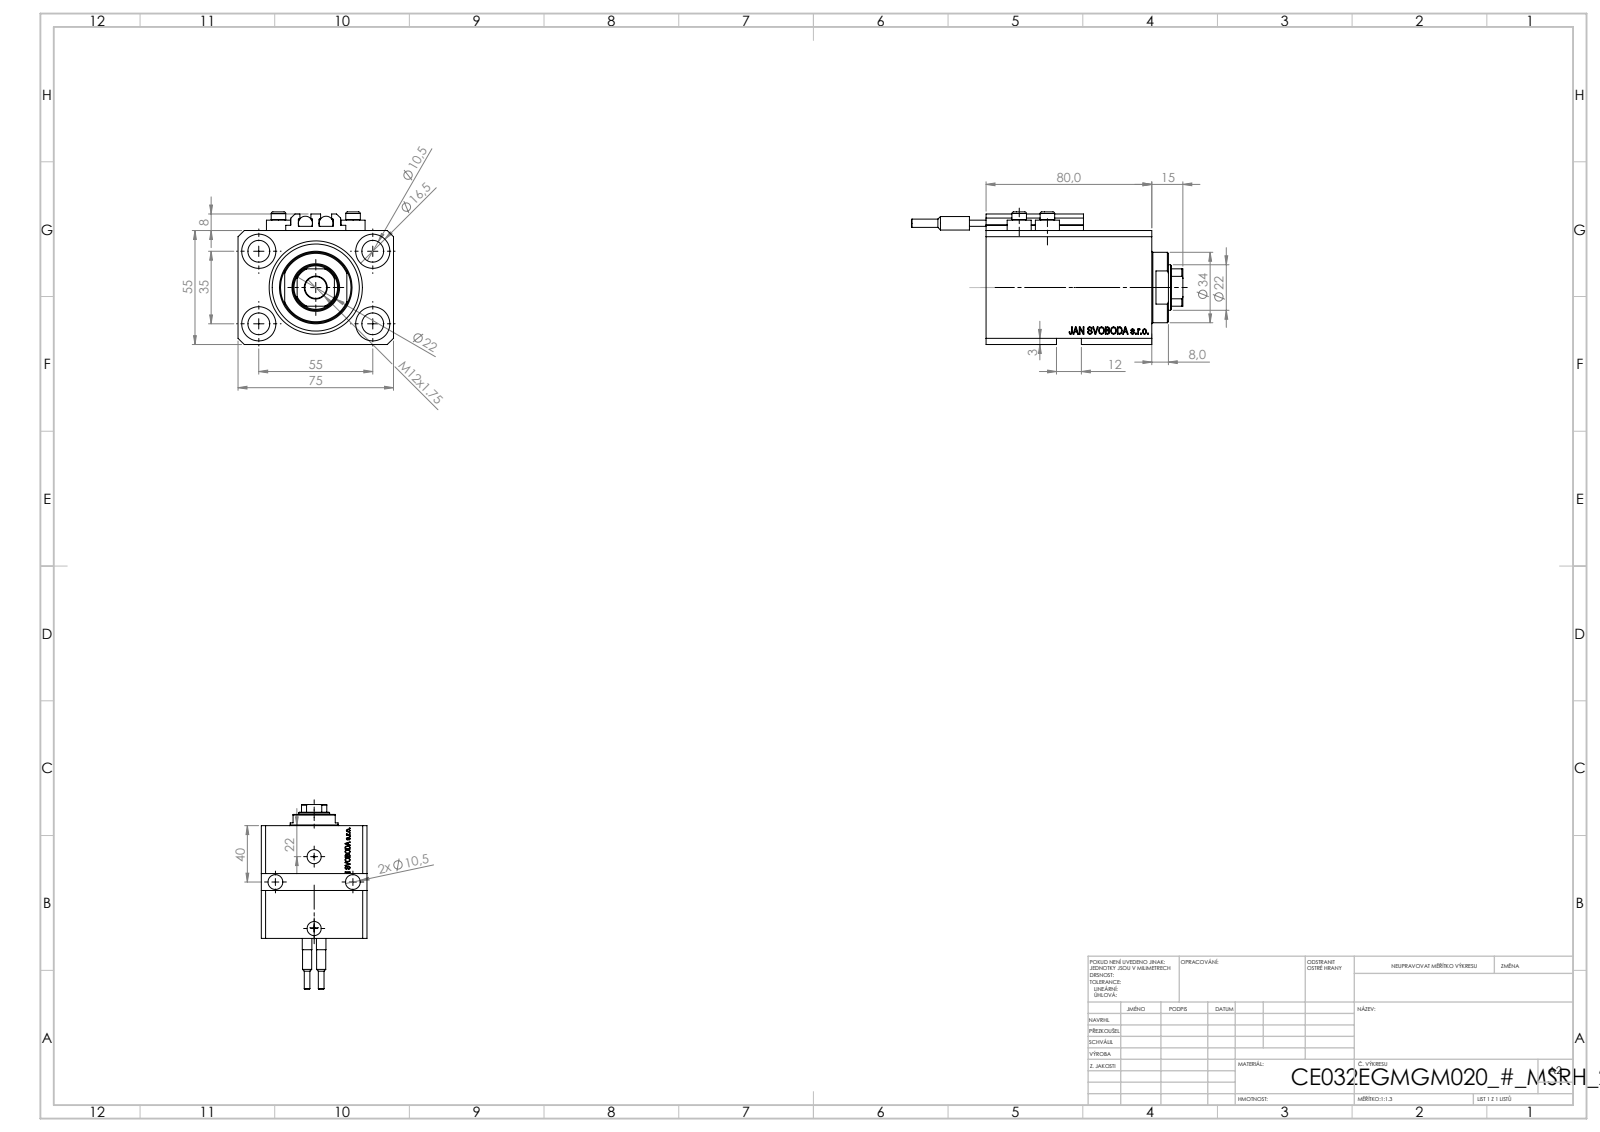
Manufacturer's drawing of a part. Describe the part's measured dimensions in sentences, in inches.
The part is named "ALLEN BOLT V250CE; V250CE_C_VCP; V250CE_E_Body; SWITCH_V250CE (+1 more)". Its 3-D file was written by "SolidWorks 2019 (CONFIG_CONTROL_DESIGN)". It is 10 solids with 1116 faces: 546 planar, 138 cylindrical and 432 other. Overall it measures 5.157 by 2.953 by 2.52 inches. Its volume is 17.54 cubic inches and its surface area 119.7 square inches. Round holes: 7 of diameter 0.413, 4 of diameter 0.049, 4 of diameter 0.157, 4 of diameter 0.65, 2 of diameter 0.394, 2 of diameter 0.518, 2 of diameter 0.787, 1 of diameter 0.866, 1 of diameter 1.26, 1 of diameter 1.772. Round bosses or shafts: 4 of diameter 0.457, 4 of diameter 0.276, 2 of diameter 0.268, 2 of diameter 0.256, 2 of diameter 0.157, 1 of diameter 1.339. Partial cylindrical surfaces (rounded edges, fillets, slot ends): 10 of radius 0.008, 1 of radius 0.413. The main face-to-face distances are 2.165, 2.953, 0.591, 0.118, 3.15, 2.559, 2.169, 0.39, 2.244, 2.76. The hole center spacings are 1.283, 2.165, 0.535, 0.555, 0.783, 0.792, 1.016, 1.121.
